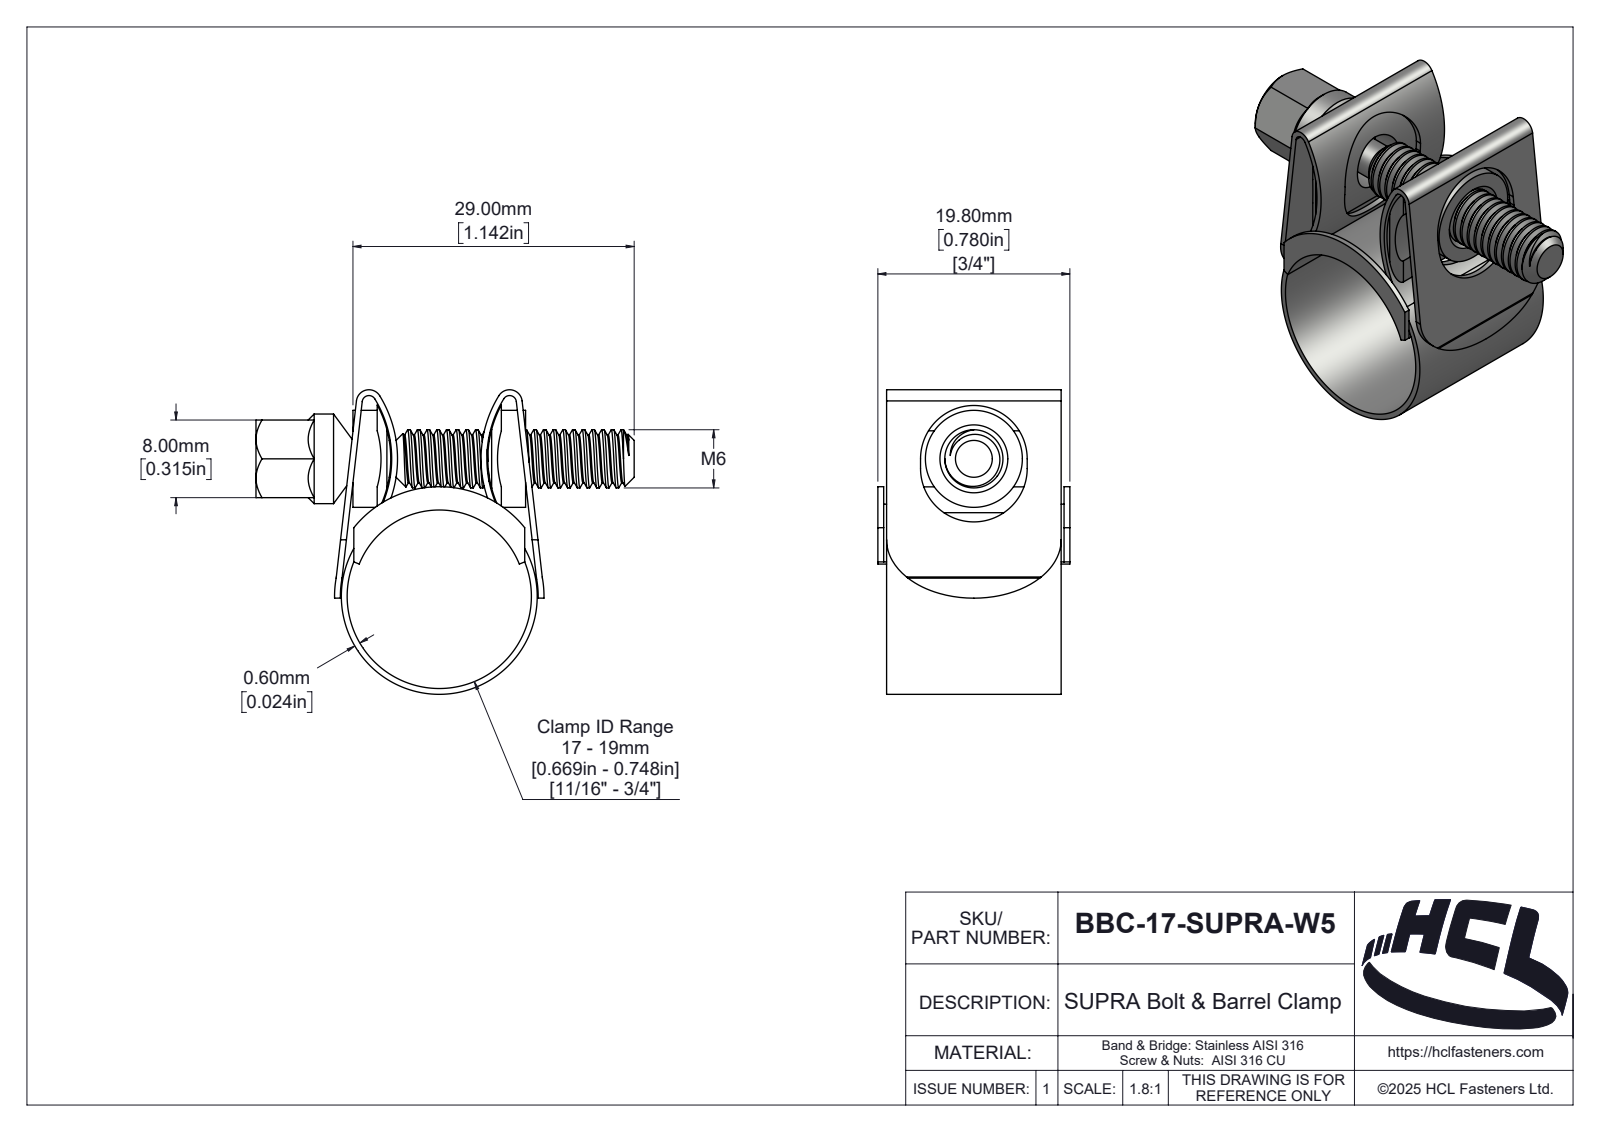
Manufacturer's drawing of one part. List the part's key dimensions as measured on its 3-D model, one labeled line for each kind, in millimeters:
Part name (STEP PRODUCT): BBC-17-SUPRA-W5
STEP written by: SolidWorks 2025 (AUTOMOTIVE_DESIGN)
Units: millimetres
Bodies: 5 solids, 283 faces (44 planar, 159 cylindrical, 80 other)
Overall size (bounding box): 39 × 31.39 × 19.8
Volume: 2 994 mm³ · Surface area: 6 800 mm²
Round holes (diameter × count): ⌀19 ×1
Round bosses / shafts (diameter × count): ⌀10 ×1, ⌀9.24 ×1, ⌀6 ×1, ⌀3.8 ×1
Partial cylindrical surfaces — rounded edges, fillets, slot ends (radius × count): R1 ×4, R0.7 ×2, R1.3 ×2, R2 ×2, R2.6 ×2, R5.5 ×2, R10.73 ×2, R11.73 ×2
Main face-to-face distances: 0.6, 0.9, 18.9, 2.5, 15.3, 19.2, 18.3, 8, 18, 12.8
